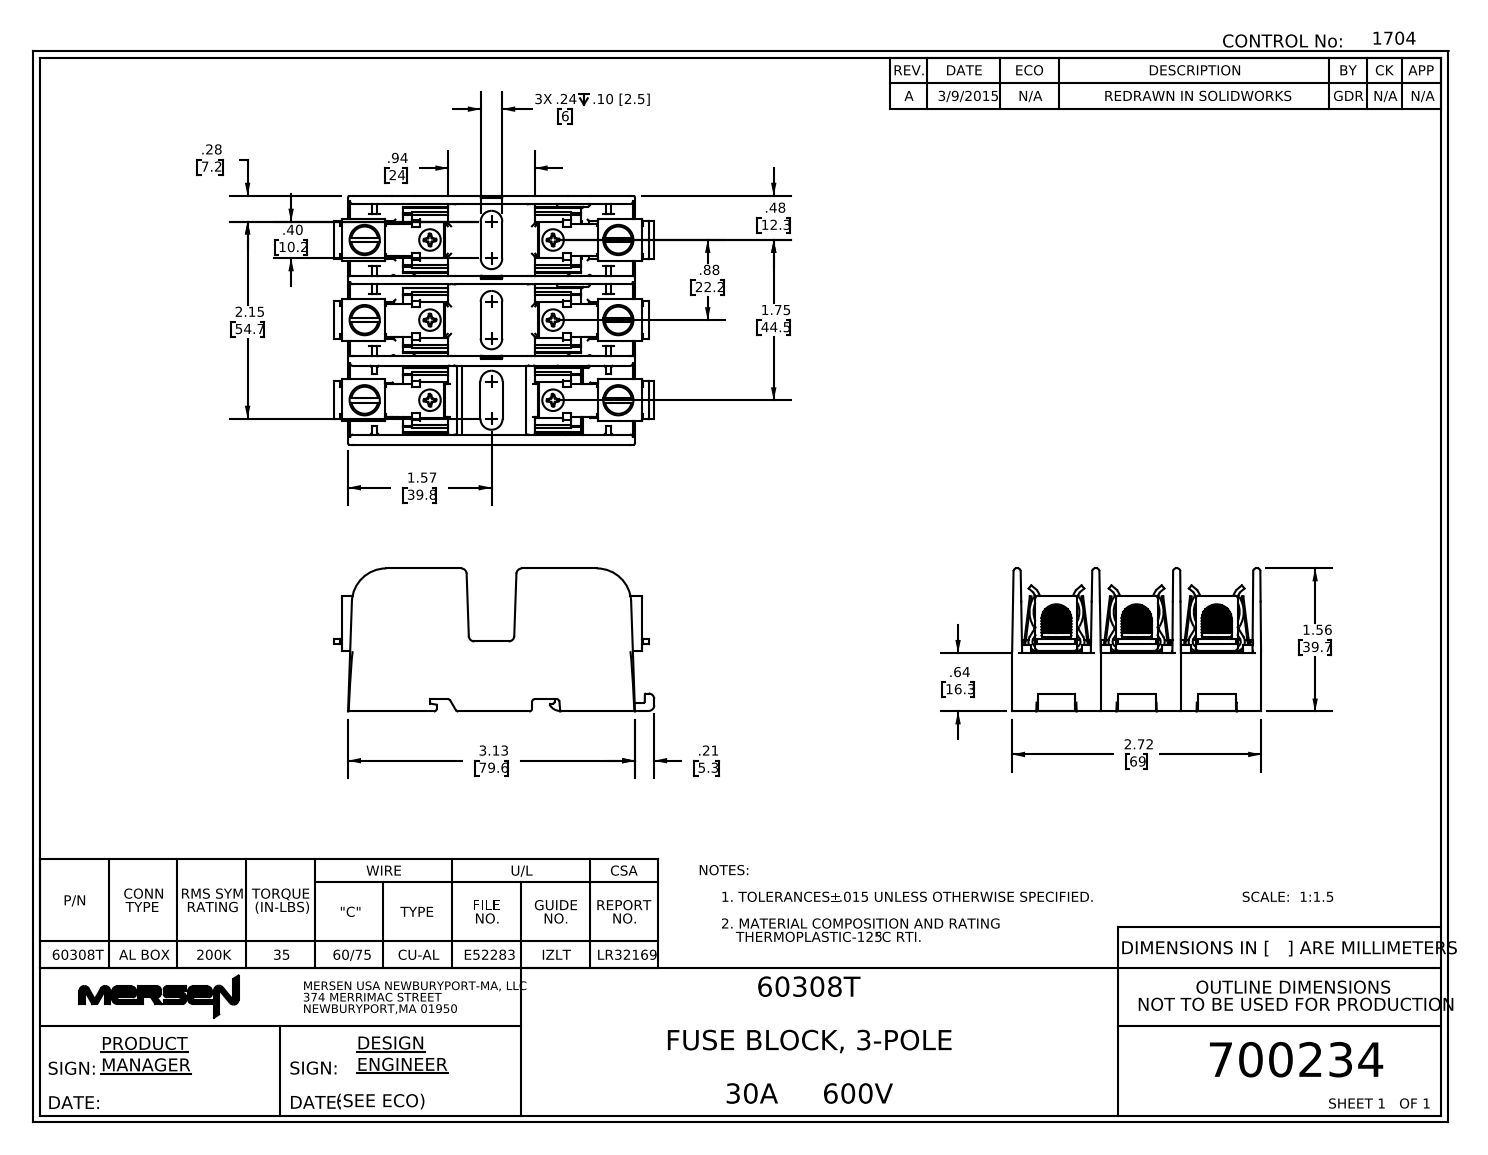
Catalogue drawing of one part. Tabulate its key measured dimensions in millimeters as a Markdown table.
| quantity | value |
| --- | --- |
| part name | 700234revA_3P |
| STEP written by | SolidWorks 2017 (AUTOMOTIVE_DESIGN) |
| units | millimeters |
| bodies | 37 solids, 2833 faces (1231 planar, 915 cylindrical, 687 other) |
| overall size | 88.8 × 69 × 39.7 |
| volume | 64 760 mm³ |
| surface area | 81 100 mm² |
| round holes (diameter × count) | 3.8 × 6, 8.4 × 6 |
| round bosses / shafts (diameter × count) | 6 × 6, 3.5 × 6, 2.1 × 6, 6.1 × 4 |
| partial cylindrical surfaces (radius × count) | 0.8 × 274, 0.4 × 49, 0.5 × 37, 0.1 × 28, 2 × 22, 0.3 × 17, 2.5 × 10, 0.7 × 8 |
| main face-to-face distances | 22.2, 1.8, 22.2, 21.8, 0.4, 49.2, 44.5, 22.1, 14.3, 18.1 |
| hole center spacings | 28.7, 56.8, 18.1, 52.2, 22.2, 22.2, 44.5, 48 |
